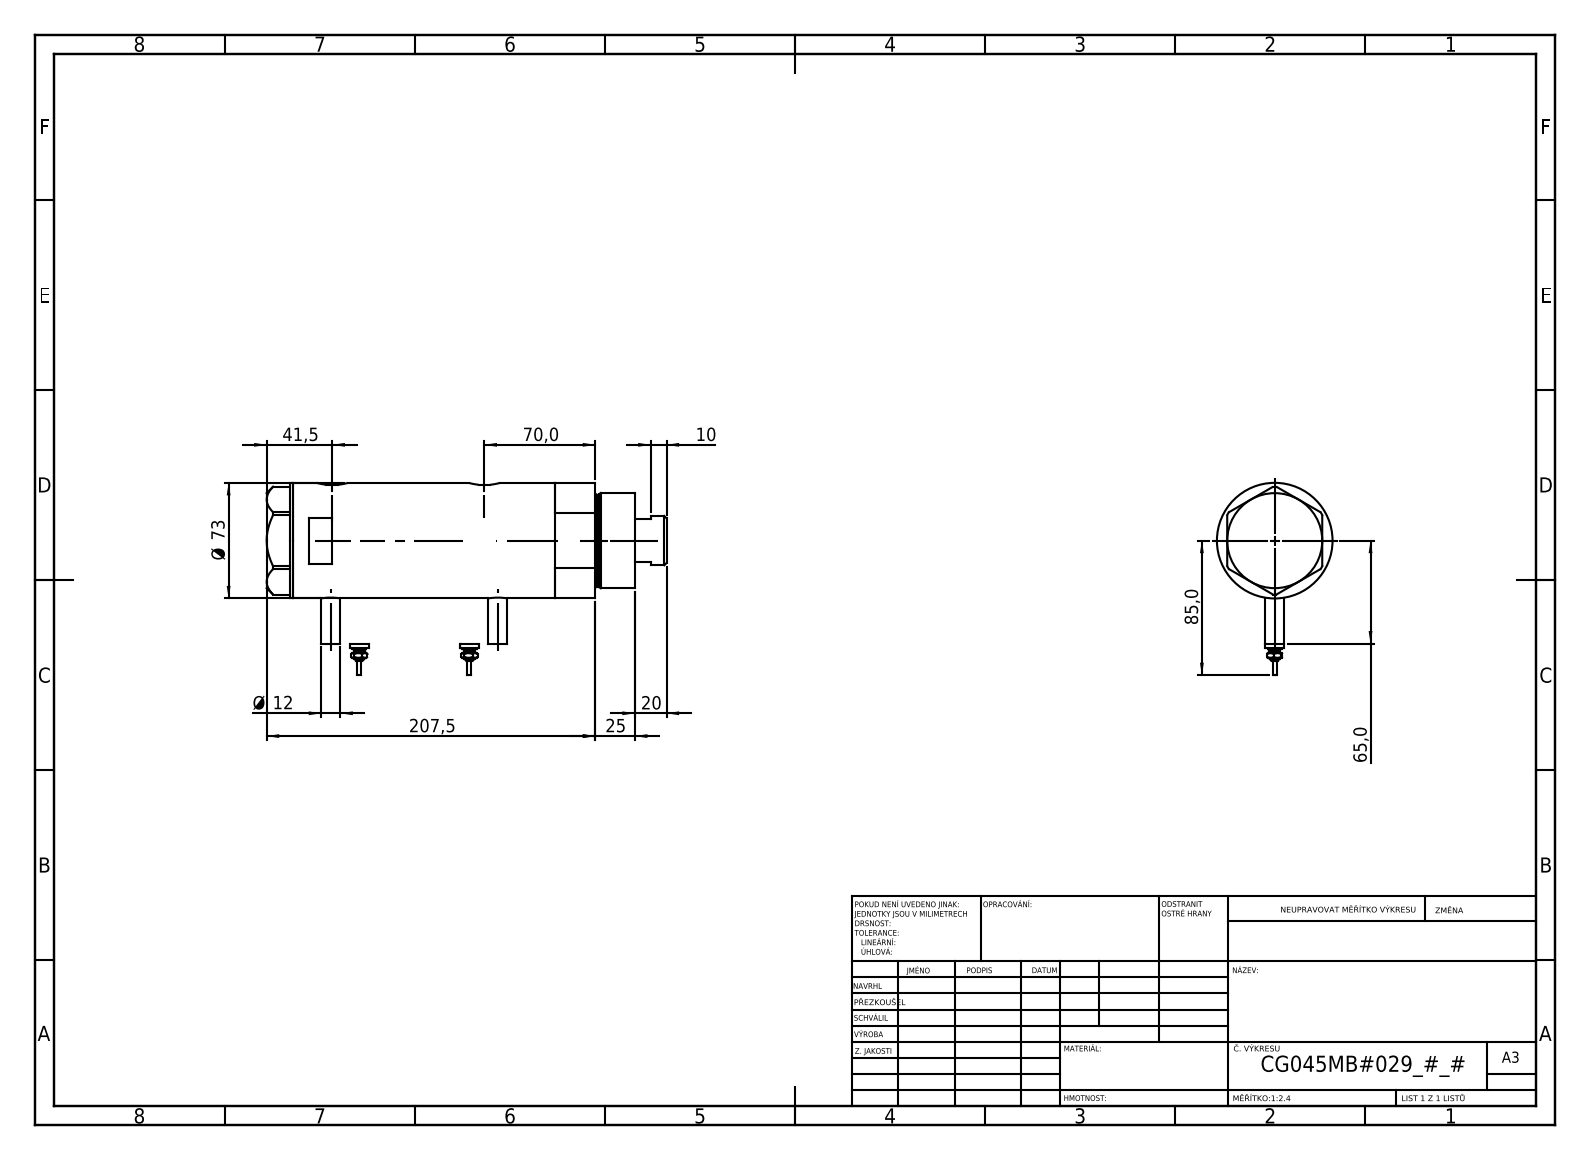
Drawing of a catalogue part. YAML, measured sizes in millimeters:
part_name: "V270CG_MIDDLE; Switch; V270CG_BACK; V270CG_VC (+1 more)"
step_written_by: "SolidWorks 2019 (CONFIG_CONTROL_DESIGN)"
units: millimeters
bodies: {solids: 6, faces: 212, planar: 77, cylindrical: 71, other: 64}
overall_size: [252.5, 121.5, 73]
volume: 908669
surface_area: 152587
round_holes:
  - {diameter: 12.5, count: 2}
  - {diameter: 13.16, count: 2}
  - {diameter: 10.5, count: 1}
  - {diameter: 32, count: 1}
  - {diameter: 33.5, count: 1}
  - {diameter: 45, count: 1}
  - {diameter: 48, count: 1}
  - {diameter: 64, count: 1}
round_bosses_or_shafts:
  - {diameter: 12, count: 4}
  - {diameter: 9, count: 2}
  - {diameter: 7, count: 2}
  - {diameter: 4.5, count: 2}
  - {diameter: 2.5, count: 2}
  - {diameter: 73, count: 1}
  - {diameter: 60, count: 1}
  - {diameter: 58, count: 1}
partial_cylinders:
  - {radius: 10, count: 2}
face_to_face_distances: [95, 121, 26, 16.5, 42.5, 137.5, 2, 216, 232.5, 190]
hole_center_spacings: [1, 8.5, 96, 97, 104.5, 105.5]
